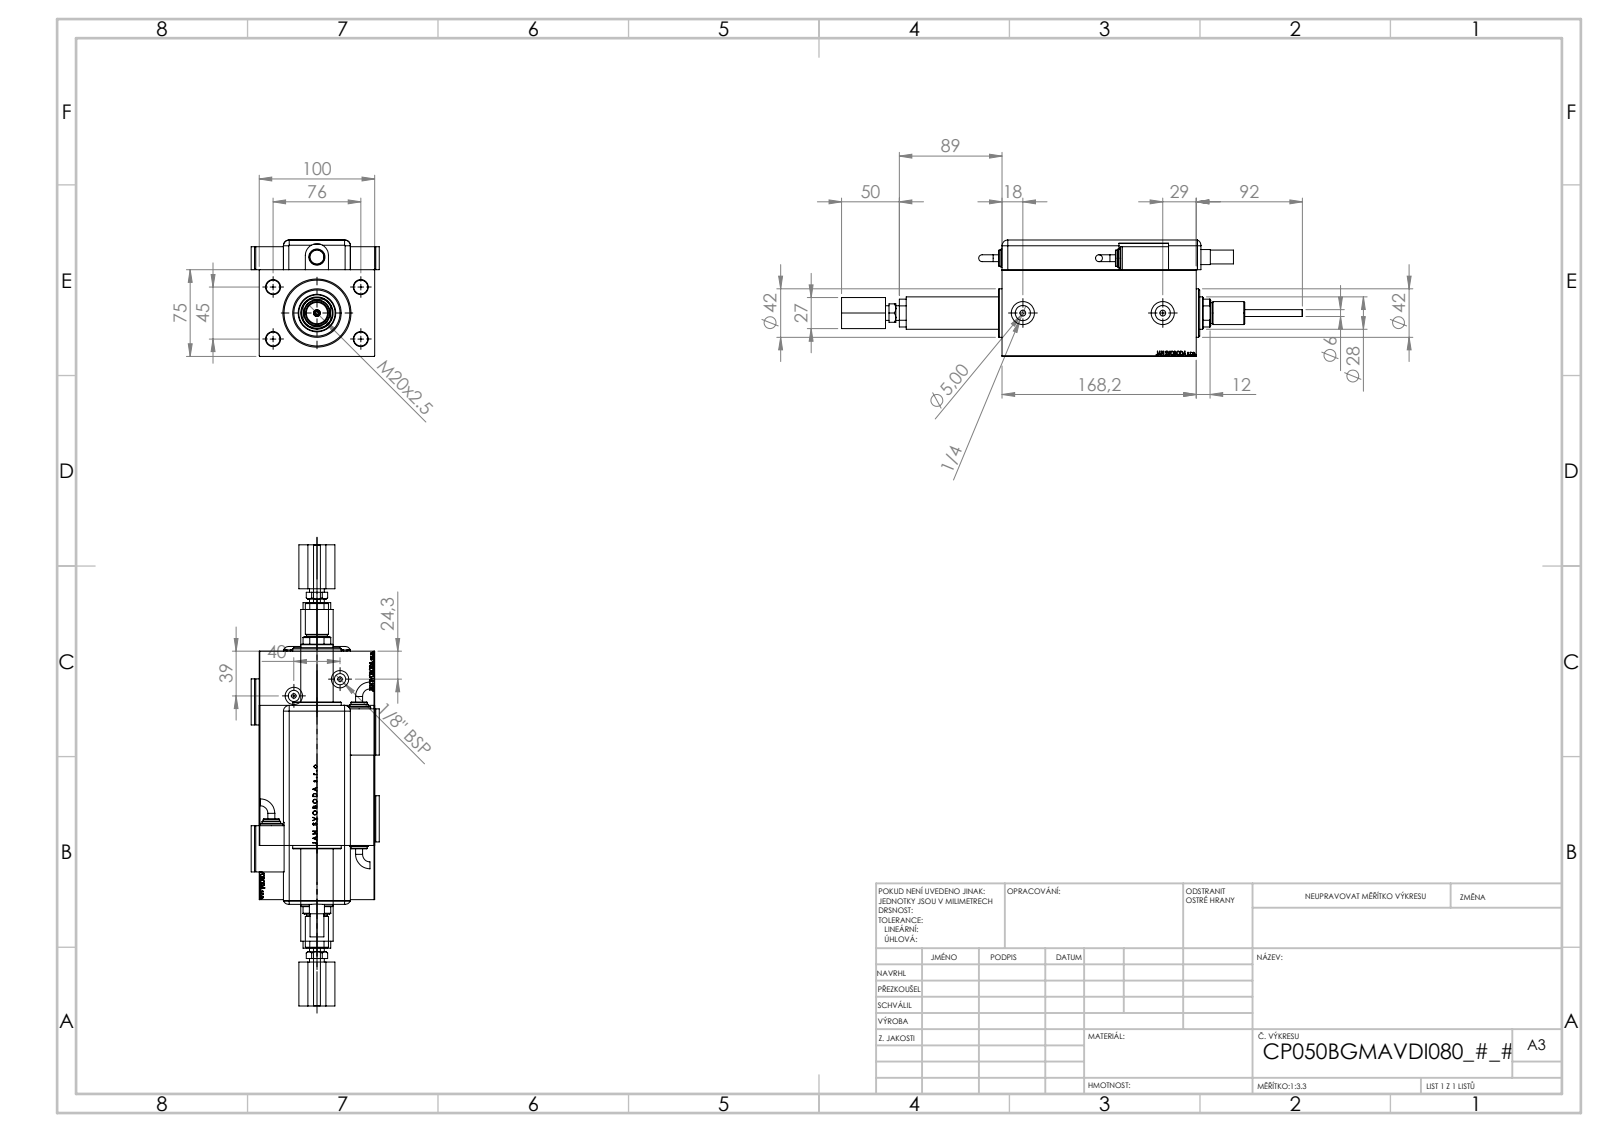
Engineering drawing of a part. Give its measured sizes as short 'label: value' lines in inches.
name: V450DCP_B_Body; V450DCP_B_RodCooling_ACCESSORIES; KRYT; V450DCP_VC_B (+6 more)
written by: SolidWorks 2019 (CONFIG_CONTROL_DESIGN)
unit: in
bodies: 11 solids, 1322 faces (618 planar, 141 cylindrical, 563 other)
size: 15.717 × 4.37 × 3.969
volume: 84.15 in³; area: 366.5 in²
holes: 4× ⌀0.157, 4× ⌀0.472, 2× ⌀0.197, 2× ⌀0.315, 2× ⌀0.383, 2× ⌀0.518, 2× ⌀0.591, 2× ⌀0.787, 1× ⌀0.118, 1× ⌀0.236, 1× ⌀0.551, 1× ⌀0.728
bosses: 3× ⌀0.787, 2× ⌀0.63, 2× ⌀0.551, 2× ⌀0.236, 1× ⌀1.654, 1× ⌀0.709, 1× ⌀0.512, 1× ⌀0.503
rounds: 9× R0.197, 1× R0.394, 1× R0.531
face distances: 2.953, 0.118, 3.937, 3.969, 1.016, 6.622, 0.945, 0.039, 3.85, 0.898
hole spacings: 1.739, 1.772, 1.813, 2.992, 3.17, 3.477, 0.787, 0.804
